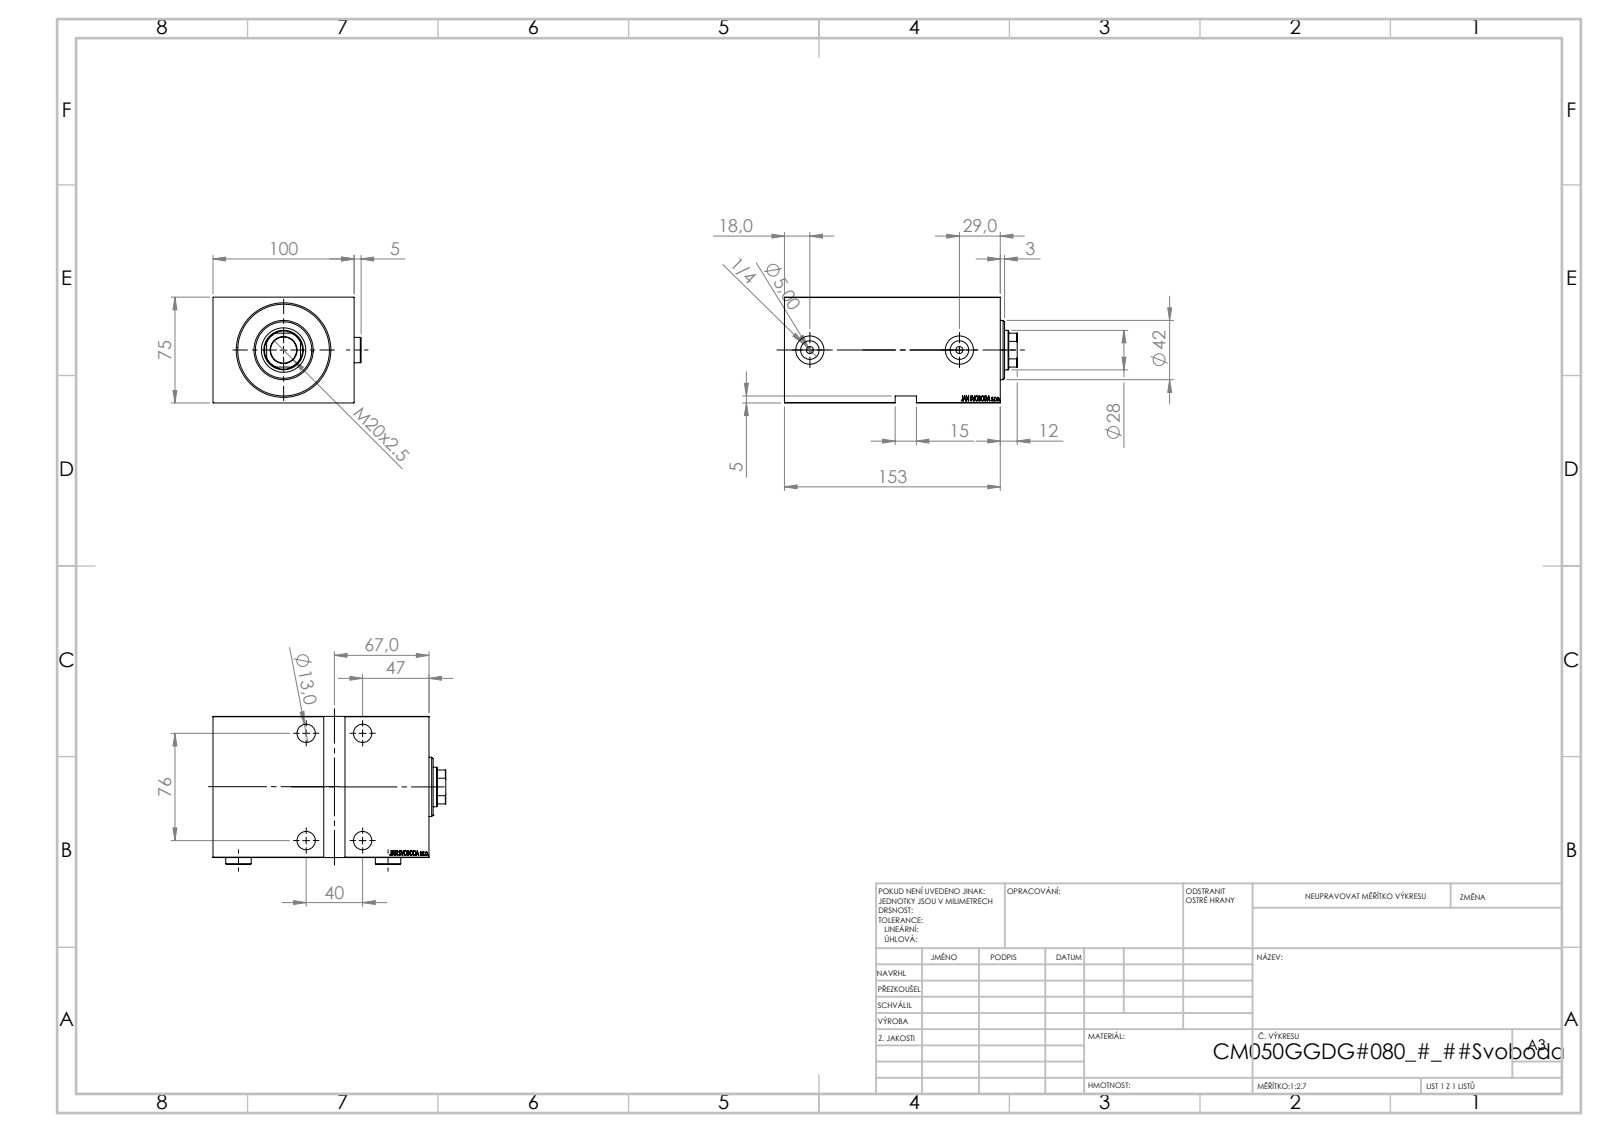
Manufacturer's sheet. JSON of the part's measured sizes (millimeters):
{"part_name": "Zatka_OIL_PORT; V450CM_VC_G; V450CM_G_VCP; V450CM_G_Body", "step_written_by": "SolidWorks 2019 (CONFIG_CONTROL_DESIGN)", "units": "millimeters", "bodies": {"solids": 5, "faces": 912, "planar": 446, "cylindrical": 68, "other": 398}, "overall_size": [165, 104.9, 75], "volume_mm3": 964500, "surface_area_mm2": 138004, "round_holes": [[13, 4], [19, 4], [5, 2], [13.16, 2], [20, 2], [18.5, 1], [28, 1], [31.5, 1], [50, 1], [52, 1], [65, 1]], "round_bosses_or_shafts": [[18, 2], [42, 1]], "partial_cylinders_radius": [[13.5, 1]], "face_to_face_distances": [75, 100, 153, 5, 14, 139, 148, 134, 87, 70], "hole_center_spacings": [40, 76, 85.88, 106]}
